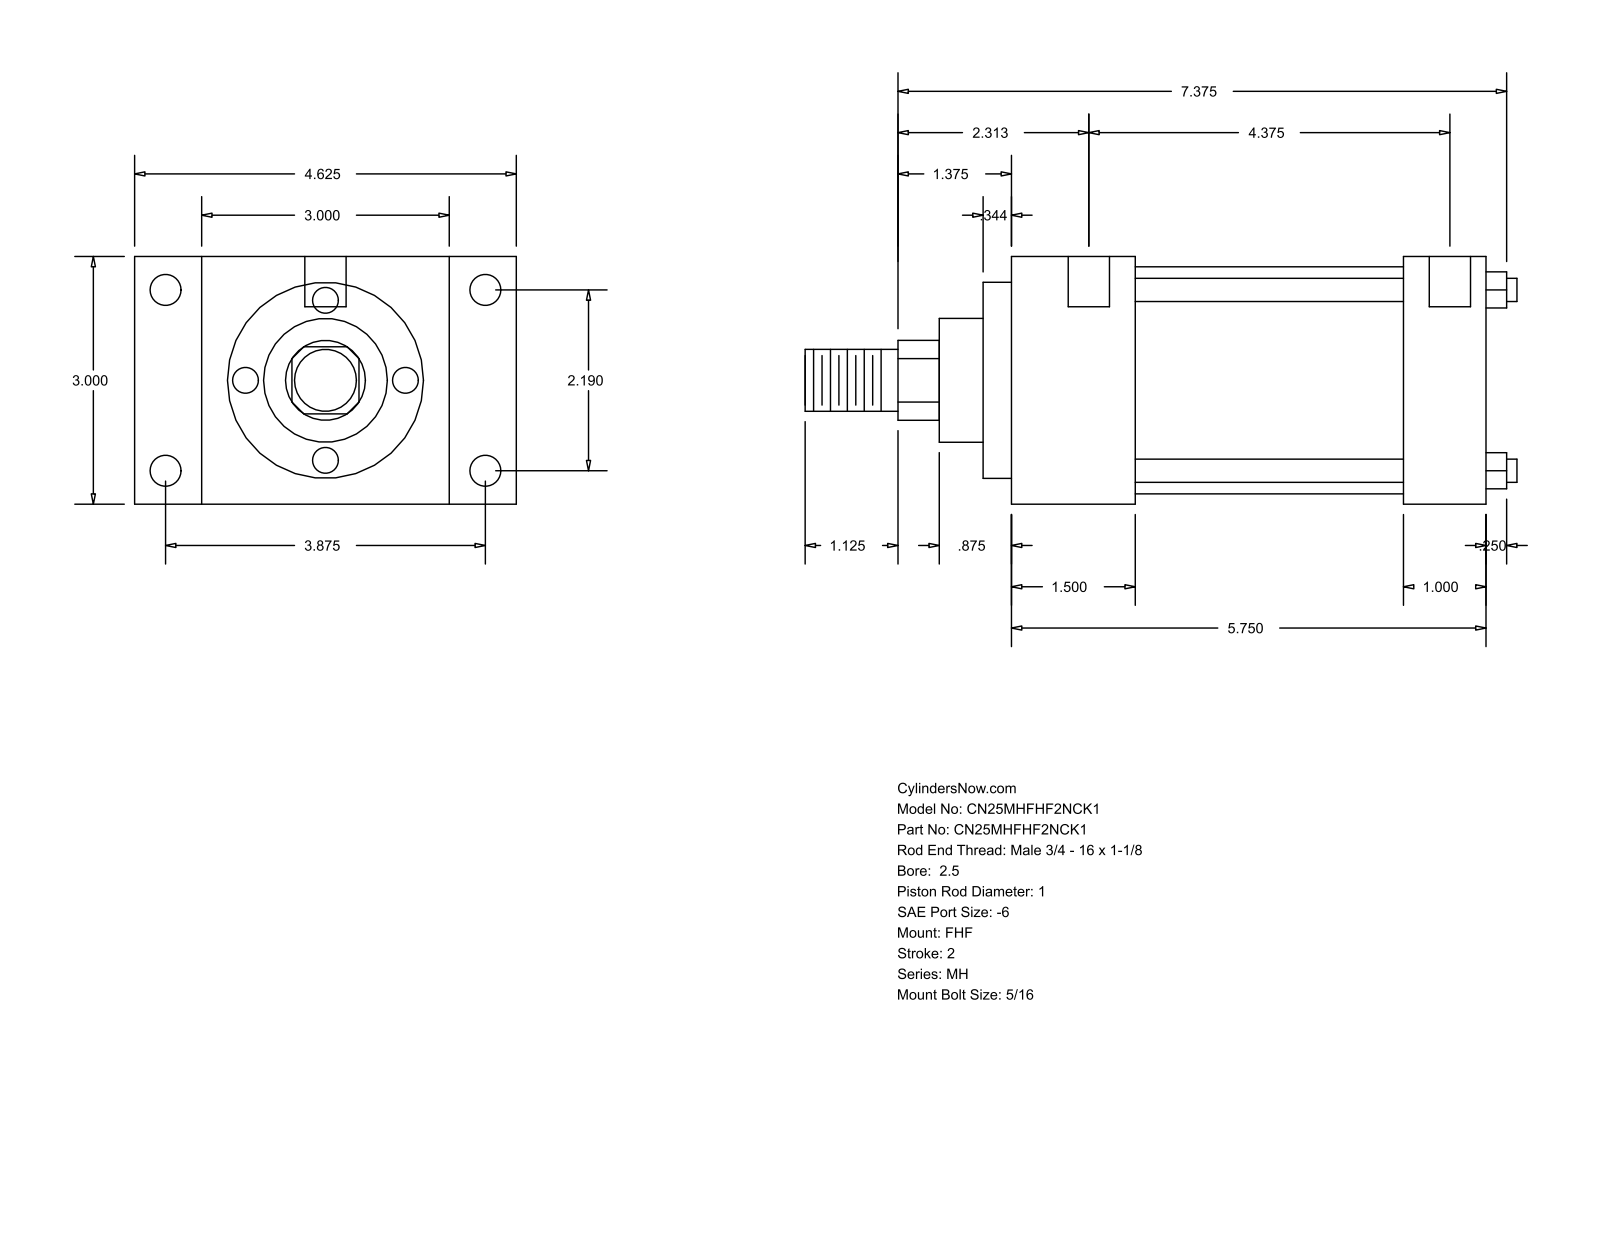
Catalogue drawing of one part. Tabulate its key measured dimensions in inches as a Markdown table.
| quantity | value |
| --- | --- |
| part name | MH_FHF__0250_1 |
| STEP written by | GSSL Pune (CONFIG_CONTROL_DESIGN) |
| units | inches |
| bodies | 0 solids, 90 faces (61 planar, 29 cylindrical, 0 other) |
| overall size | 8.625 × 4.625 × 3 |
| round holes (diameter × count) | 0.219 × 4, 0.375 × 4, 0.5 × 2 |
| round bosses / shafts (diameter × count) | 0.281 × 4, 2.75 × 1, 2.375 × 1, 1.5 × 1, 1 × 1, 0.75 × 1 |
| partial cylindrical surfaces (radius × count) | 0.484 × 1 |
| main face-to-face distances | 3, 5.75, 1.5, 4.25, 0.813, 3.813, 4.625, 4.75, 3.25, 1 |
| hole center spacings | 2.19, 3.875, 4.451, 4.687, 0.125, 0.187, 4.375, 4.5 |
